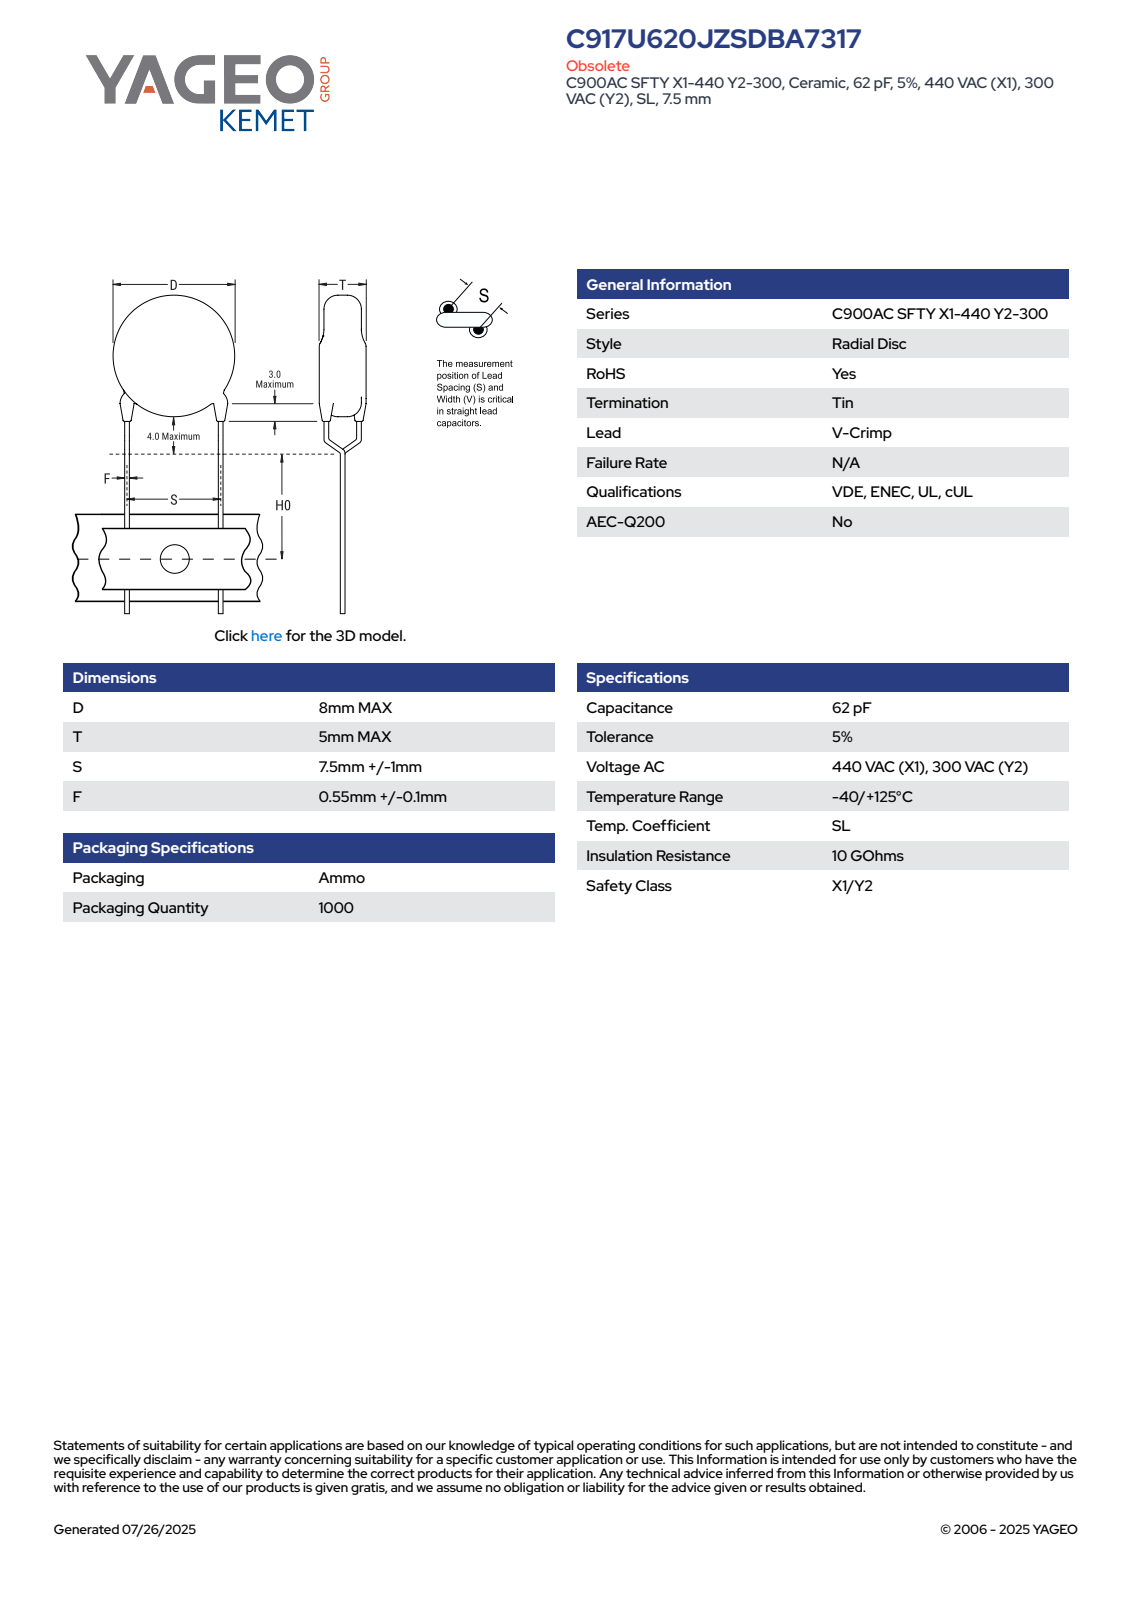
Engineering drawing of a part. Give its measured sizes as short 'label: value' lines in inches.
name: CCD_VCC900_D8T5S7.5LL20F0.65
written by: SolidWorks 2014 (AUTOMOTIVE_DESIGN)
unit: in
bodies: 5 solids, 93 faces (65 planar, 16 cylindrical, 12 other)
size: 1.252 × 0.321 × 0.197
volume: 0.016 in³; area: 0.494 in²
bosses: 6× ⌀0.026, 1× ⌀0.315
face distances: 0.197, 0.902, 0.041, 1.115, 0.213, 1.074, 0.172, 0.033, 0.018, 0.015
